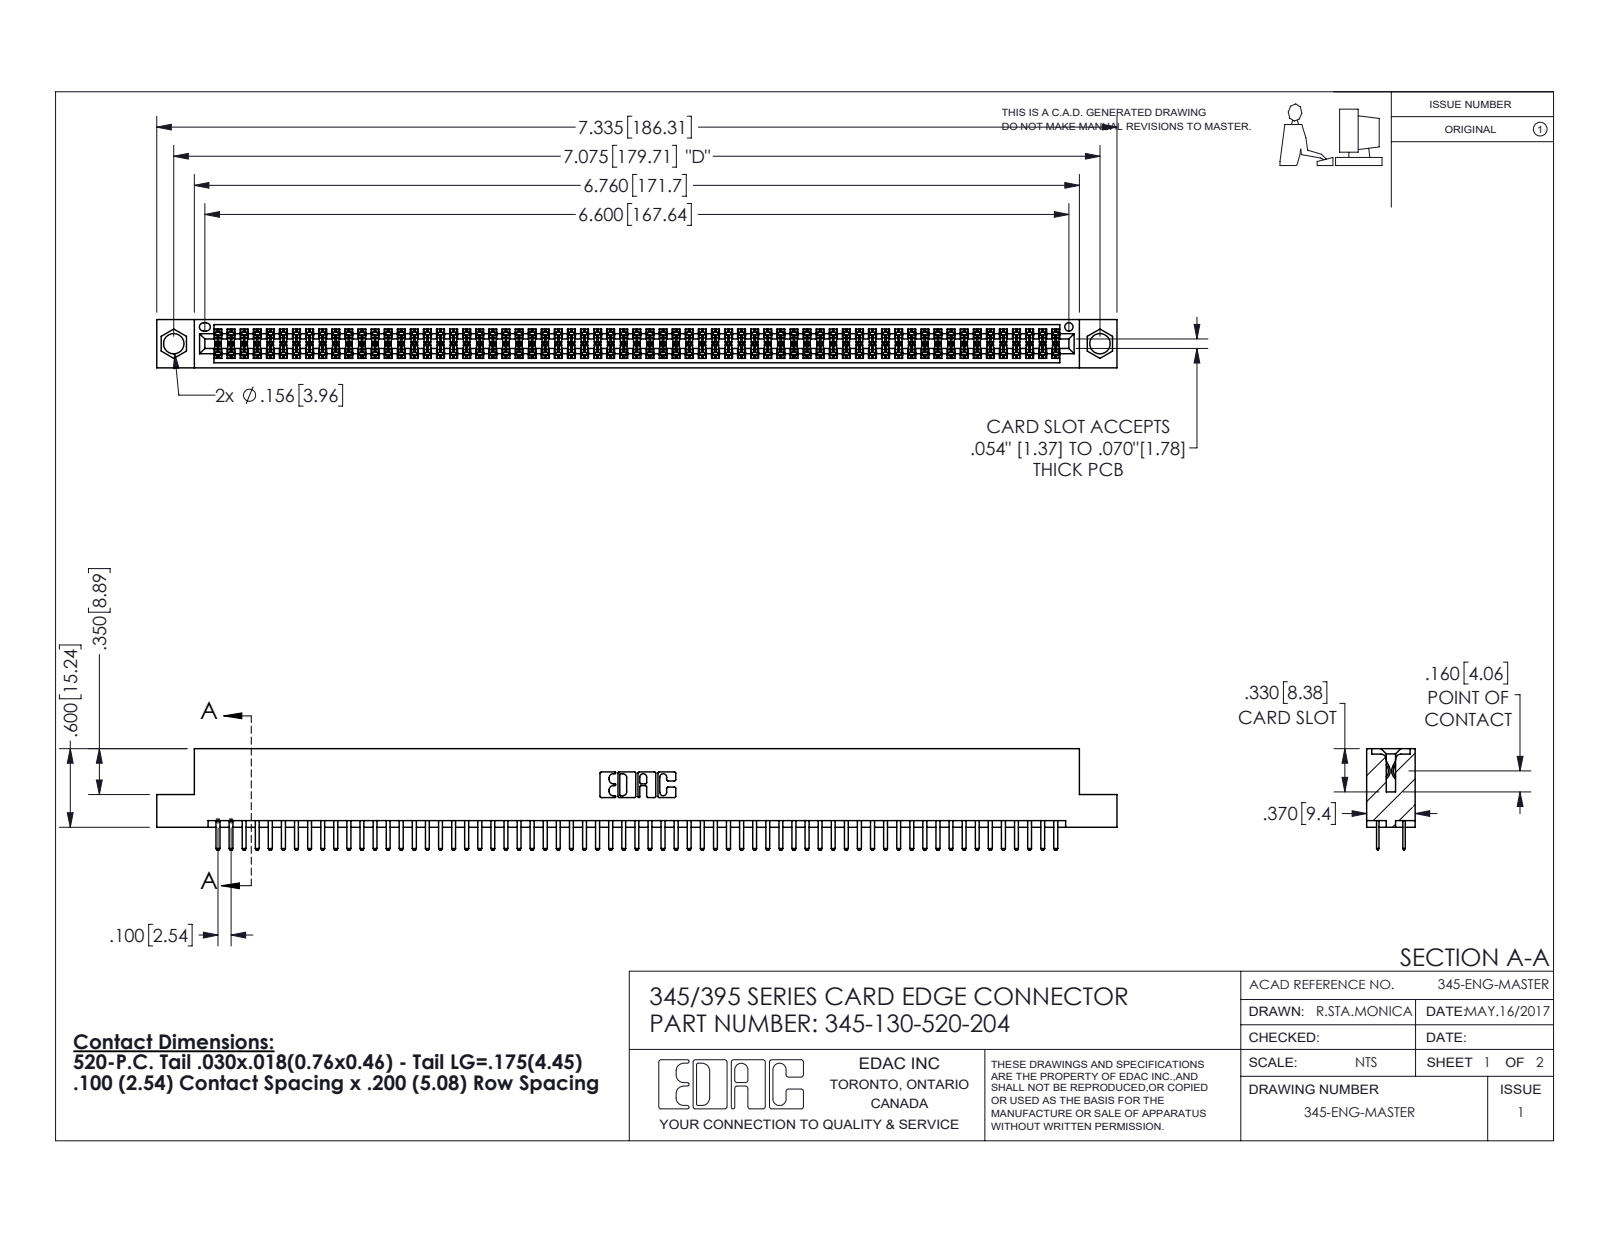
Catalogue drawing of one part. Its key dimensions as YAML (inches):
part_name: "345 Part_Flush Mounting Lugs - 0.156 Dia-TI; 345-130-520-204; 345-292-001_345-293-120"
step_written_by: "SolidWorks 2020 (CONFIG_CONTROL_DESIGN)"
units: inches
bodies: {solids: 131, faces: 7160, planar: 4644, cylindrical: 2516, other: 0}
overall_size: [7.335, 0.775, 0.37]
volume: 1.107
surface_area: 41.85
round_holes:
  - {diameter: 0.156, count: 2}
  - {diameter: 0.064, count: 1}
partial_cylinders:
  - {radius: 0.006, count: 195}
  - {radius: 0.01, count: 134}
  - {radius: 0.01, count: 22}
  - {radius: 0.007, count: 6}
  - {radius: 0.031, count: 6}
  - {radius: 0.026, count: 3}
  - {radius: 0.014, count: 2}
  - {radius: 0.019, count: 2}
face_to_face_distances: [0.072, 0.298, 0.2, 0.37, 0.098, 0.272, 0.025, 0.225, 0.022, 0.072]
hole_center_spacings: [0.27, 6.839, 7.075]
